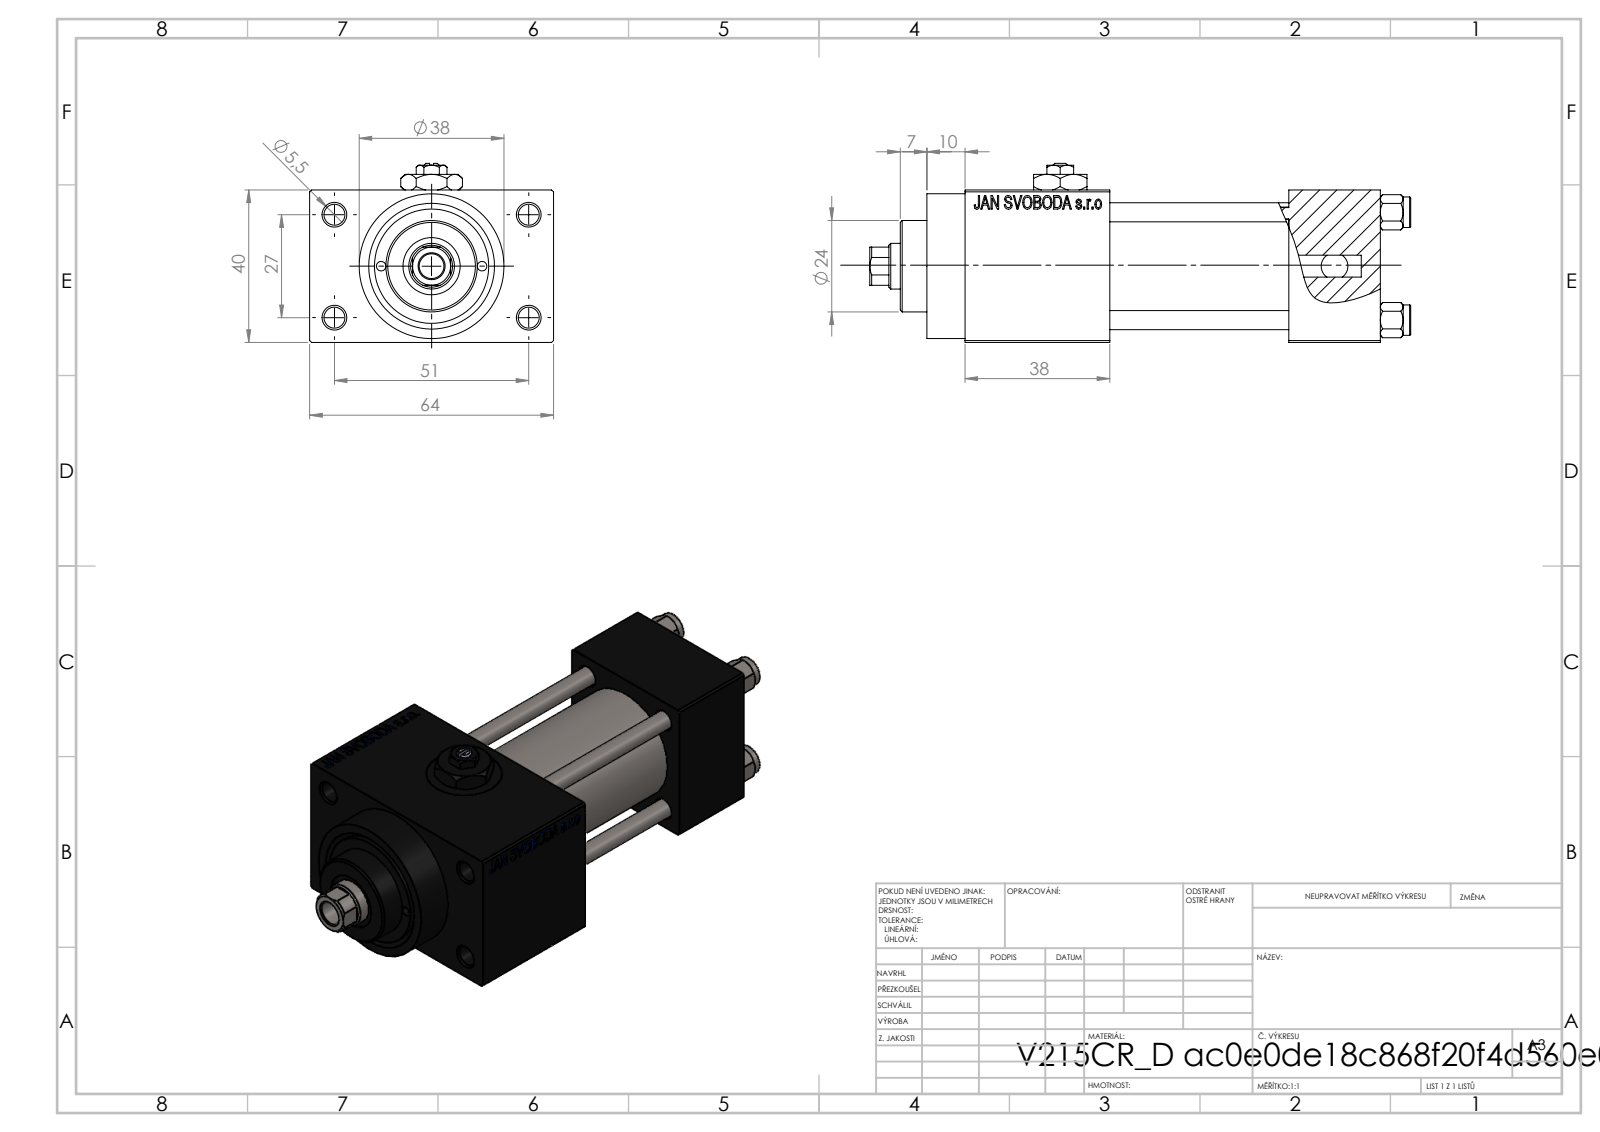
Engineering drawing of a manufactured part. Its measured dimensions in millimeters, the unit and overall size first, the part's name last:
Units: millimetres
Overall size (bounding box): 142 × 64 × 47
Round holes (diameter × count): ⌀5 ×4, ⌀5.5 ×4, ⌀20 ×4, ⌀13.16 ×3, ⌀2.5 ×2, ⌀7 ×2, ⌀6.5 ×1, ⌀12 ×1, ⌀15 ×1, ⌀25 ×1, ⌀30 ×1
Round bosses / shafts (diameter × count): ⌀8 ×4, ⌀38 ×1, ⌀31 ×1, ⌀24 ×1
Partial cylindrical surfaces — rounded edges, fillets, slot ends (radius × count): R5.5 ×1
Main face-to-face distances: 40, 12, 47, 24, 71, 52, 38, 85, 109, 64
Hole centre spacings: 11.37, 14.18, 18.23, 20.01, 28.3, 28.85, 29.89, 30.84
Volume: 173 578 mm³ · Surface area: 62 721 mm²
Bodies: 12 solids, 1157 faces (521 planar, 96 cylindrical, 540 other)
Part name (STEP PRODUCT): V215_VC_A; V215CR_VCP_D; V215CR_D_TYCINKA; V215CR_D_Body (+2 more)
STEP written by: SolidWorks 2019 (CONFIG_CONTROL_DESIGN)
